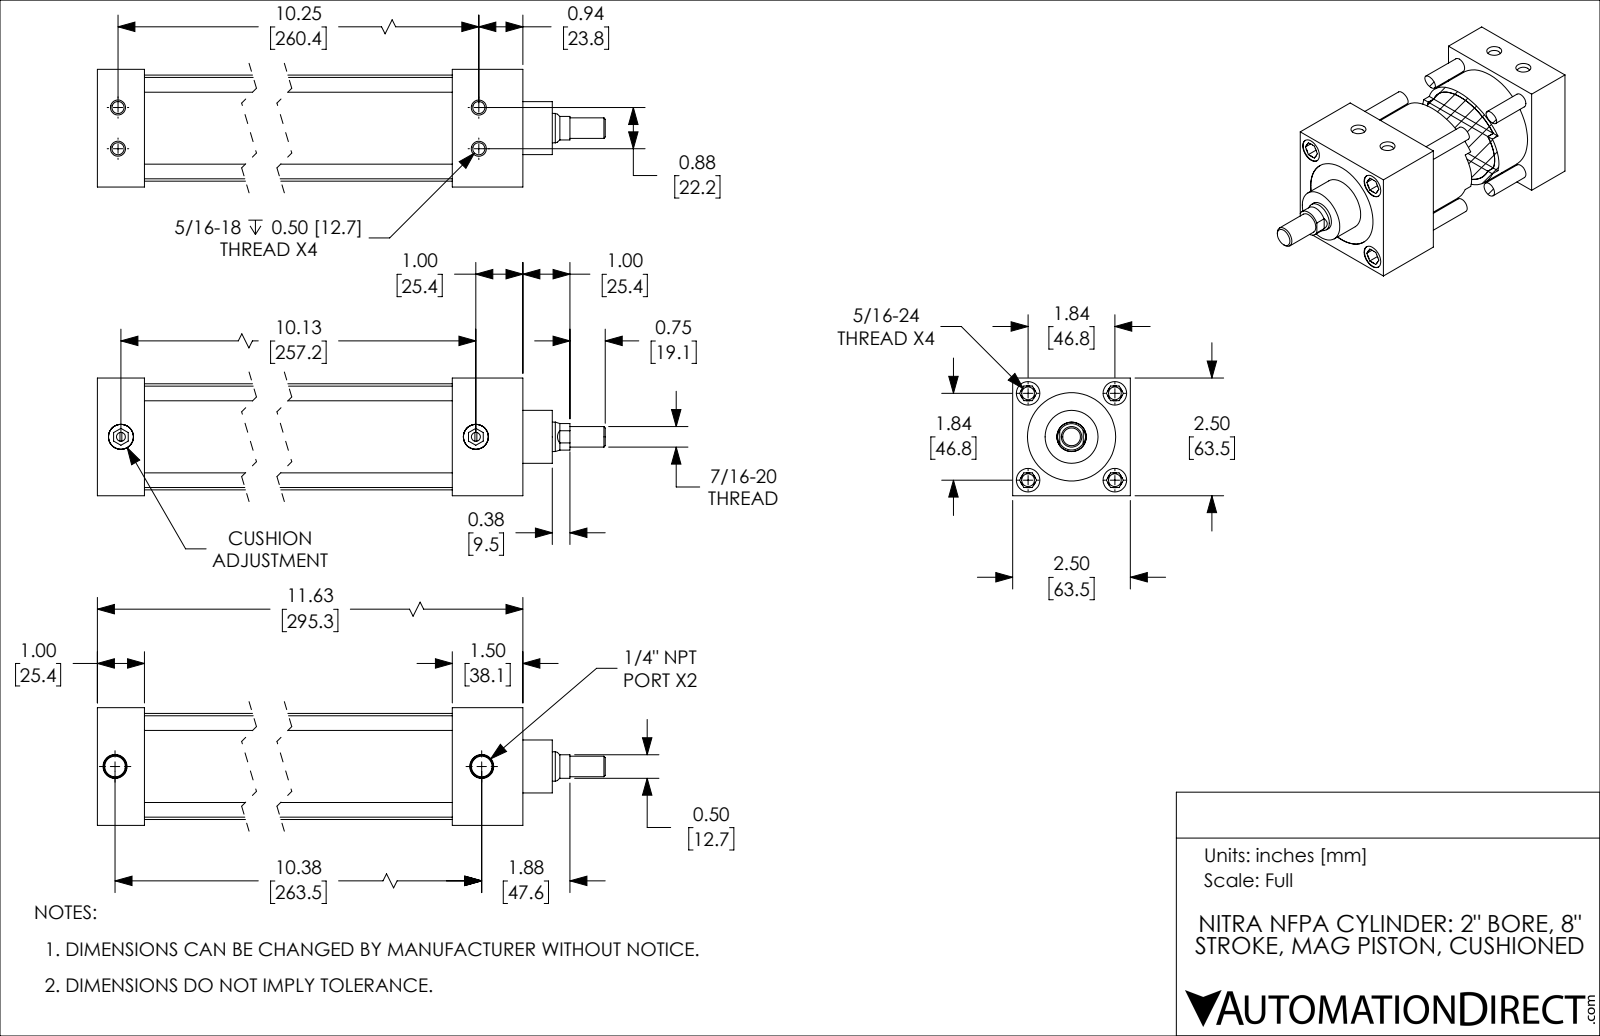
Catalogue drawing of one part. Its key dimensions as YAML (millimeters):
part_name: "D232080DT-MC_CUSHION; D232080DT-MC_PISTON_KK1; D232080DT-MC; D232080DT-MC_BODY"
step_written_by: "SolidWorks 2019 (CONFIG_CONTROL_DESIGN)"
units: millimeters
bodies: {solids: 4, faces: 248, planar: 90, cylindrical: 78, other: 80}
overall_size: [339.7, 63.5, 63.5]
volume: 524400
surface_area: 166300
round_holes:
  - {diameter: 6.9, count: 7}
  - {diameter: 6.5, count: 4}
  - {diameter: 12.7, count: 4}
  - {diameter: 4.8, count: 2}
  - {diameter: 11.1, count: 2}
  - {diameter: 13.5, count: 2}
  - {diameter: 15.9, count: 1}
  - {diameter: 47.6, count: 1}
  - {diameter: 50.8, count: 1}
round_bosses_or_shafts:
  - {diameter: 7.9, count: 4}
  - {diameter: 13.5, count: 2}
  - {diameter: 57.2, count: 1}
  - {diameter: 50.8, count: 1}
  - {diameter: 28.6, count: 1}
  - {diameter: 15.8, count: 1}
  - {diameter: 11.1, count: 1}
partial_cylinders:
  - {radius: 7.1, count: 1}
face_to_face_distances: [63.5, 25.4, 257.2, 231.8, 54, 28.6, 203.2, 295.3, 269.9, 241.3]
hole_center_spacings: [46.7, 46.8, 33, 11.2, 11.3, 22.2, 33.1, 66.1]
